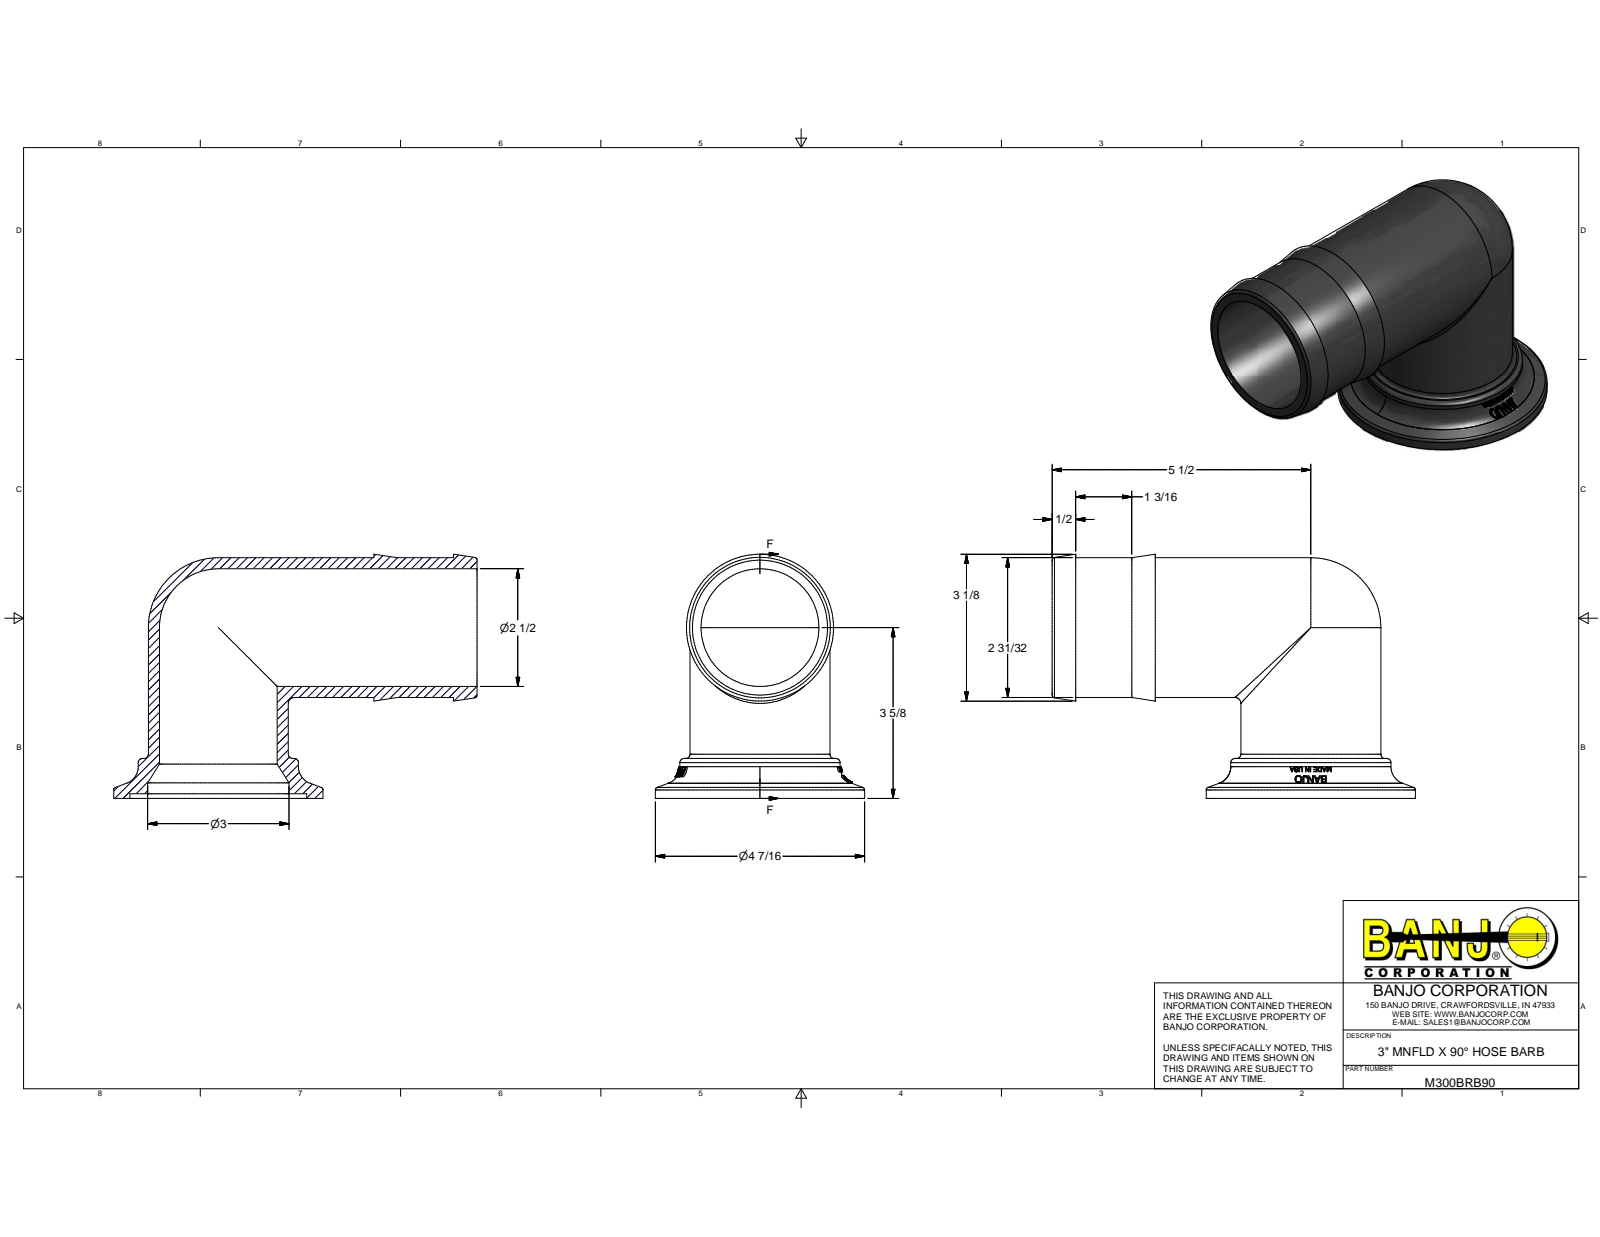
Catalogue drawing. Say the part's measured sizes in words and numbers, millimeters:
The part is named "M300BRB90". Its 3-D file was written by "Autodesk Inventor 2014 (AUTOMOTIVE_DESIGN)". It is 1 solid with 407 faces: 173 planar, 9 cylindrical and 225 other. Overall it measures 195.83 by 131.83 by 112.78 millimeters. Its volume is 341 407 cubic millimeters and its surface area 113 064 square millimeters. Round holes: 2 of diameter 63.5, 1 of diameter 76.2, 1 of diameter 95.25. Round bosses or shafts: 2 of diameter 75.44, 1 of diameter 112.78, 1 of diameter 86.36. The main face-to-face distances are 2.54, 21.59, 19.05, 42.93, 55.63, 12.7, 0.49, 14.36, 6.96, 4.76.
